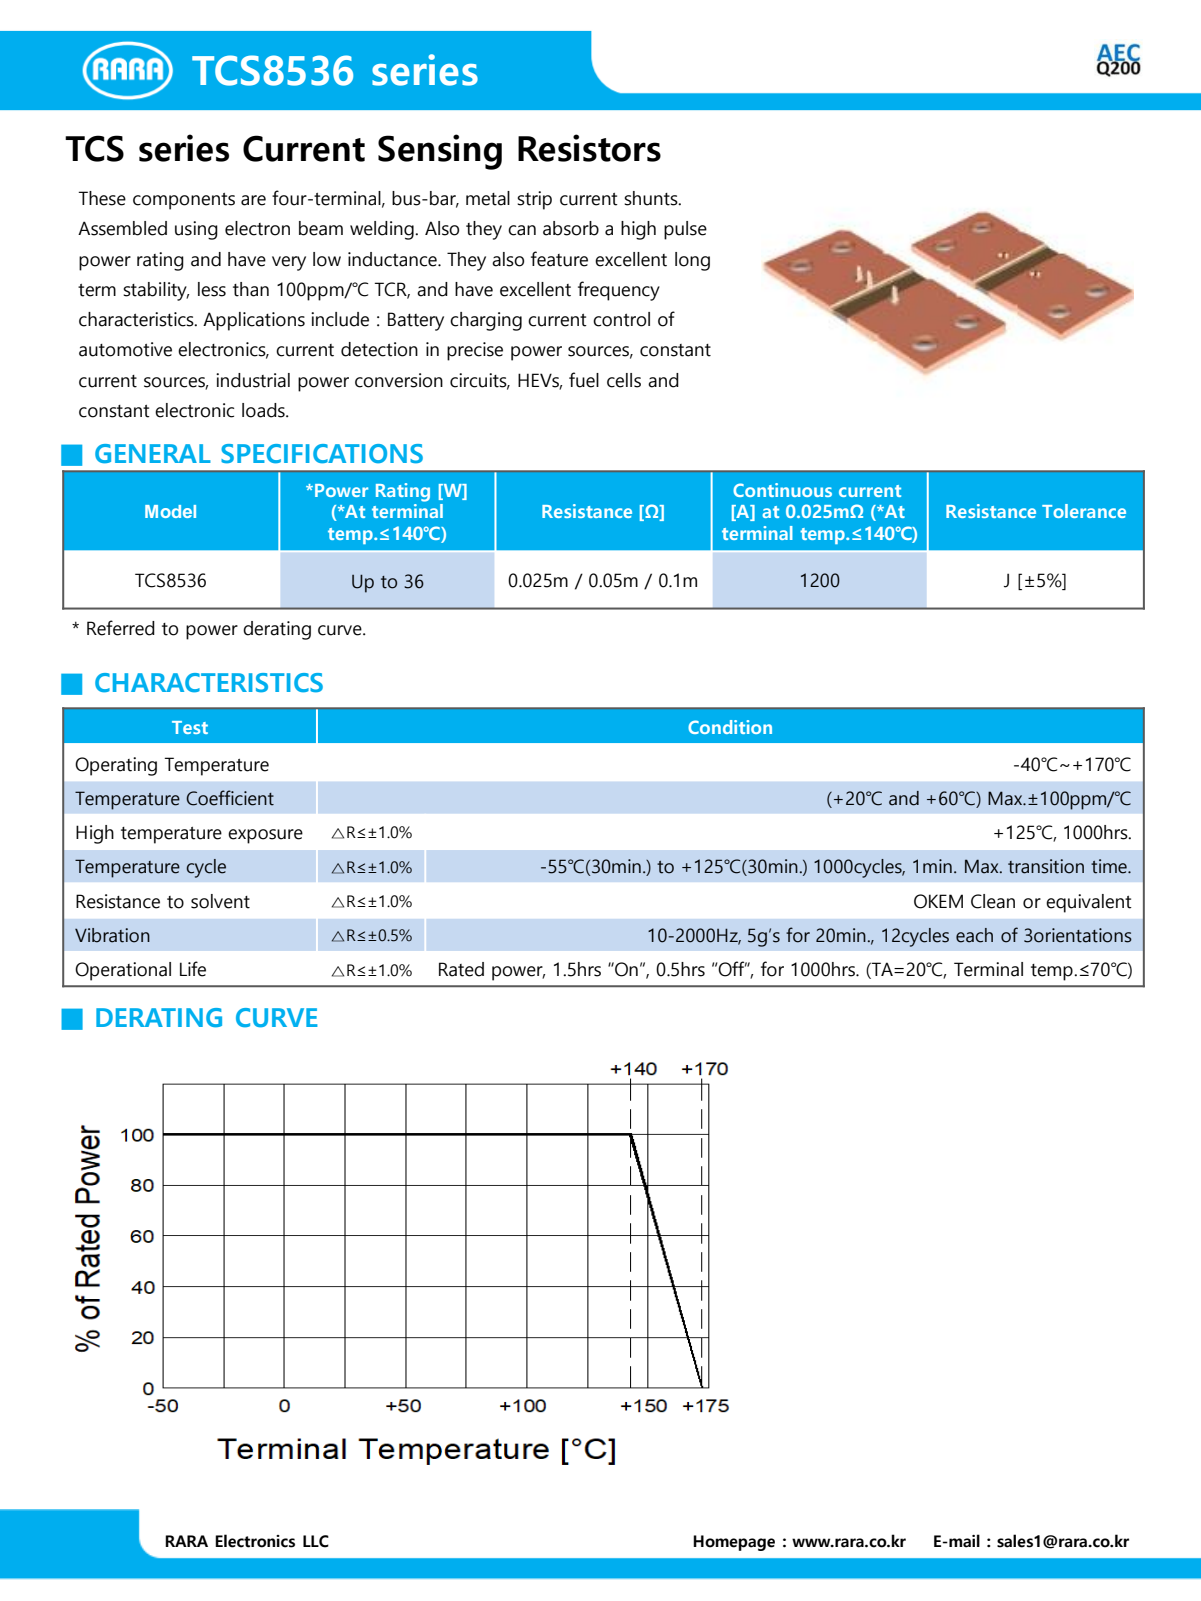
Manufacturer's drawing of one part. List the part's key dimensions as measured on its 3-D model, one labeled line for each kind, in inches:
Part name (STEP PRODUCT): Left Terminal WSBS 8536 25 microohm; WSBS8536 25 microohm; Right Terminal WSBS 8536 25 microohm; Element WSBS 8536 25 microohm
STEP written by: SolidWorks 2019 (AUTOMOTIVE_DESIGN)
Units: inches
Bodies: 3 solids, 26 faces (22 planar, 4 cylindrical, 0 other)
Overall size (bounding box): 3.346 × 1.417 × 0.118
Volume: 0.52 in³ · Surface area: 10.88 in²
Round holes (diameter × count): ⌀0.394 ×2
Main face-to-face distances: 0.118, 1.417, 1.6, 1.746, 0.145, 0.078, 0.04, 3.346, 3.201, 3.256
Hole centre spacings: 2.362
